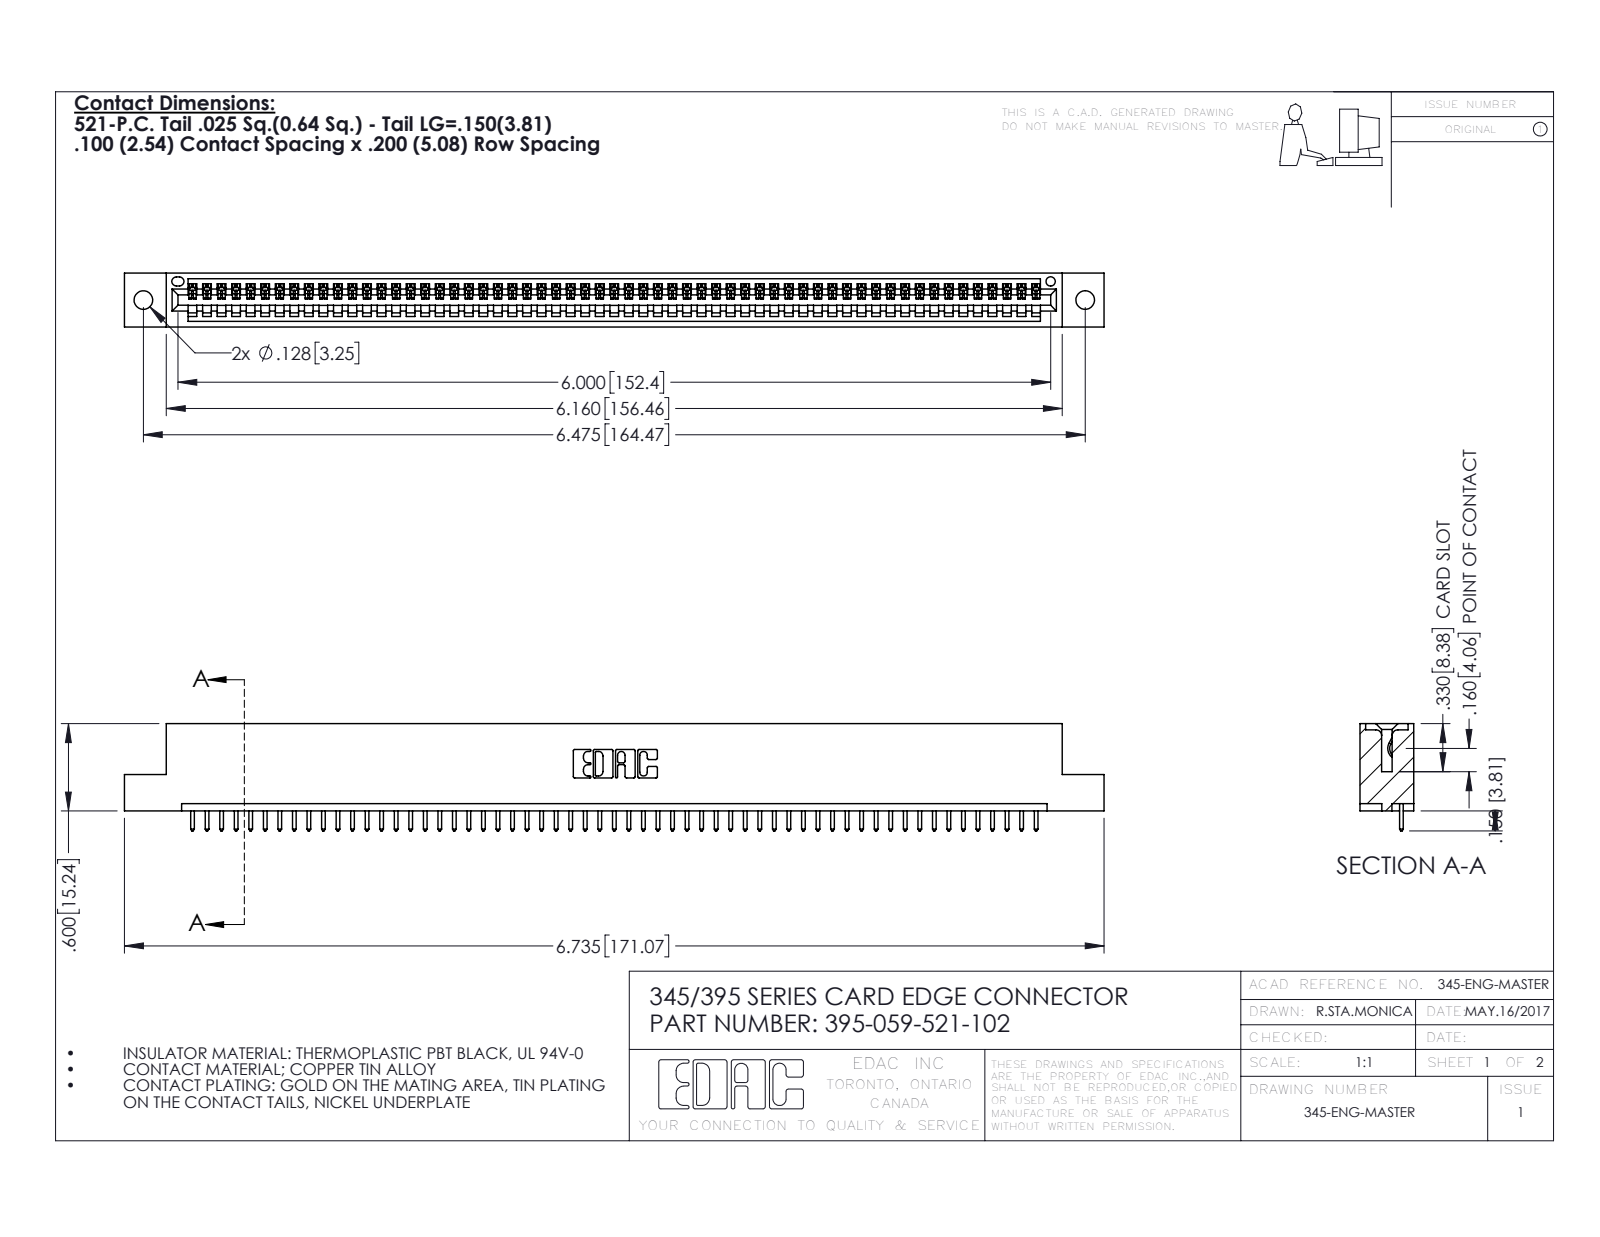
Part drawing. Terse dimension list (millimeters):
name: 345-292-001_345-293-121; 345 Part_Flush Mounting Lugs - 0.128 Dia; 395-059-521-102
written by: SolidWorks 2016 (CONFIG_CONTROL_DESIGN)
unit: mm
bodies: 60 solids, 3548 faces (2440 planar, 1108 cylindrical, 0 other)
size: 171.1 × 18.7 × 9.4
volume: 16 200 mm³; area: 20 810 mm²
holes: 2× ⌀3.3, 1× ⌀1.6
rounds: 118× R0.2, 118× R0.3, 22× R0.3, 6× R0.2, 6× R0.8, 3× R0.7, 2× R0.8, 2× R1
face distances: 7.6, 1.8, 9.4, 5.1, 2.5, 6.9, 0.6, 5.7, 3.8, 1.8
hole spacings: 6.9, 158.5, 164.5
